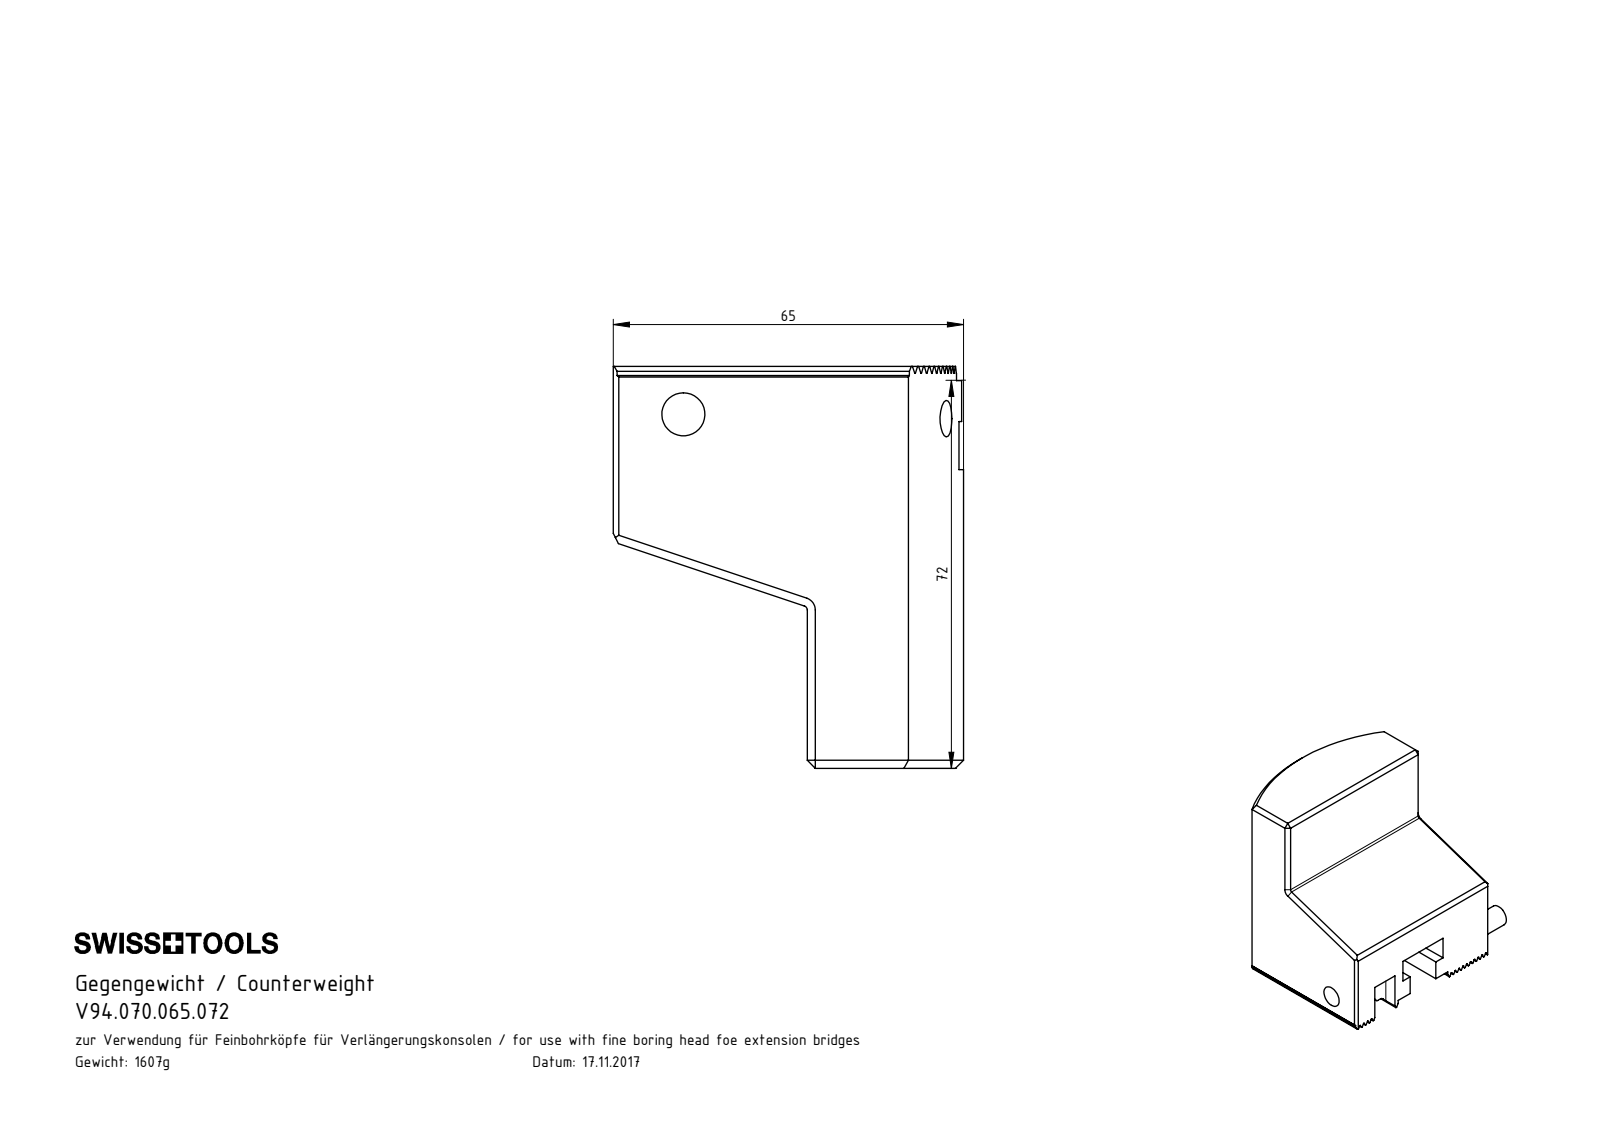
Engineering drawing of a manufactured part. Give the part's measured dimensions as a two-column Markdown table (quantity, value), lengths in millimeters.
| quantity | value |
| --- | --- |
| part name | F0U.ER1.001.074; ISO 4028 - M8 x 35; F0U-ER1.001.074_C; ISO 8734 - 8 x 20 m6 |
| STEP written by | SolidWorks 2017 (AUTOMOTIVE_DESIGN) |
| units | millimeters |
| bodies | 3 solids, 152 faces (111 planar, 31 cylindrical, 10 other) |
| overall size | 82 × 74.58 × 65 |
| volume | 204 701 mm³ |
| surface area | 31 291 mm² |
| round holes (diameter × count) | 8 × 2, 6.8 × 1 |
| round bosses / shafts (diameter × count) | 8 × 1, 5.5 × 1 |
| partial cylindrical surfaces (radius × count) | 0.14 × 22, 0.8 × 1, 5.25 × 1, 65 × 1 |
| main face-to-face distances | 70, 1.73, 8.66, 36, 55.43, 6.93, 3.46, 5.2, 43.3, 24.5 |
| hole center spacings | 7 |
